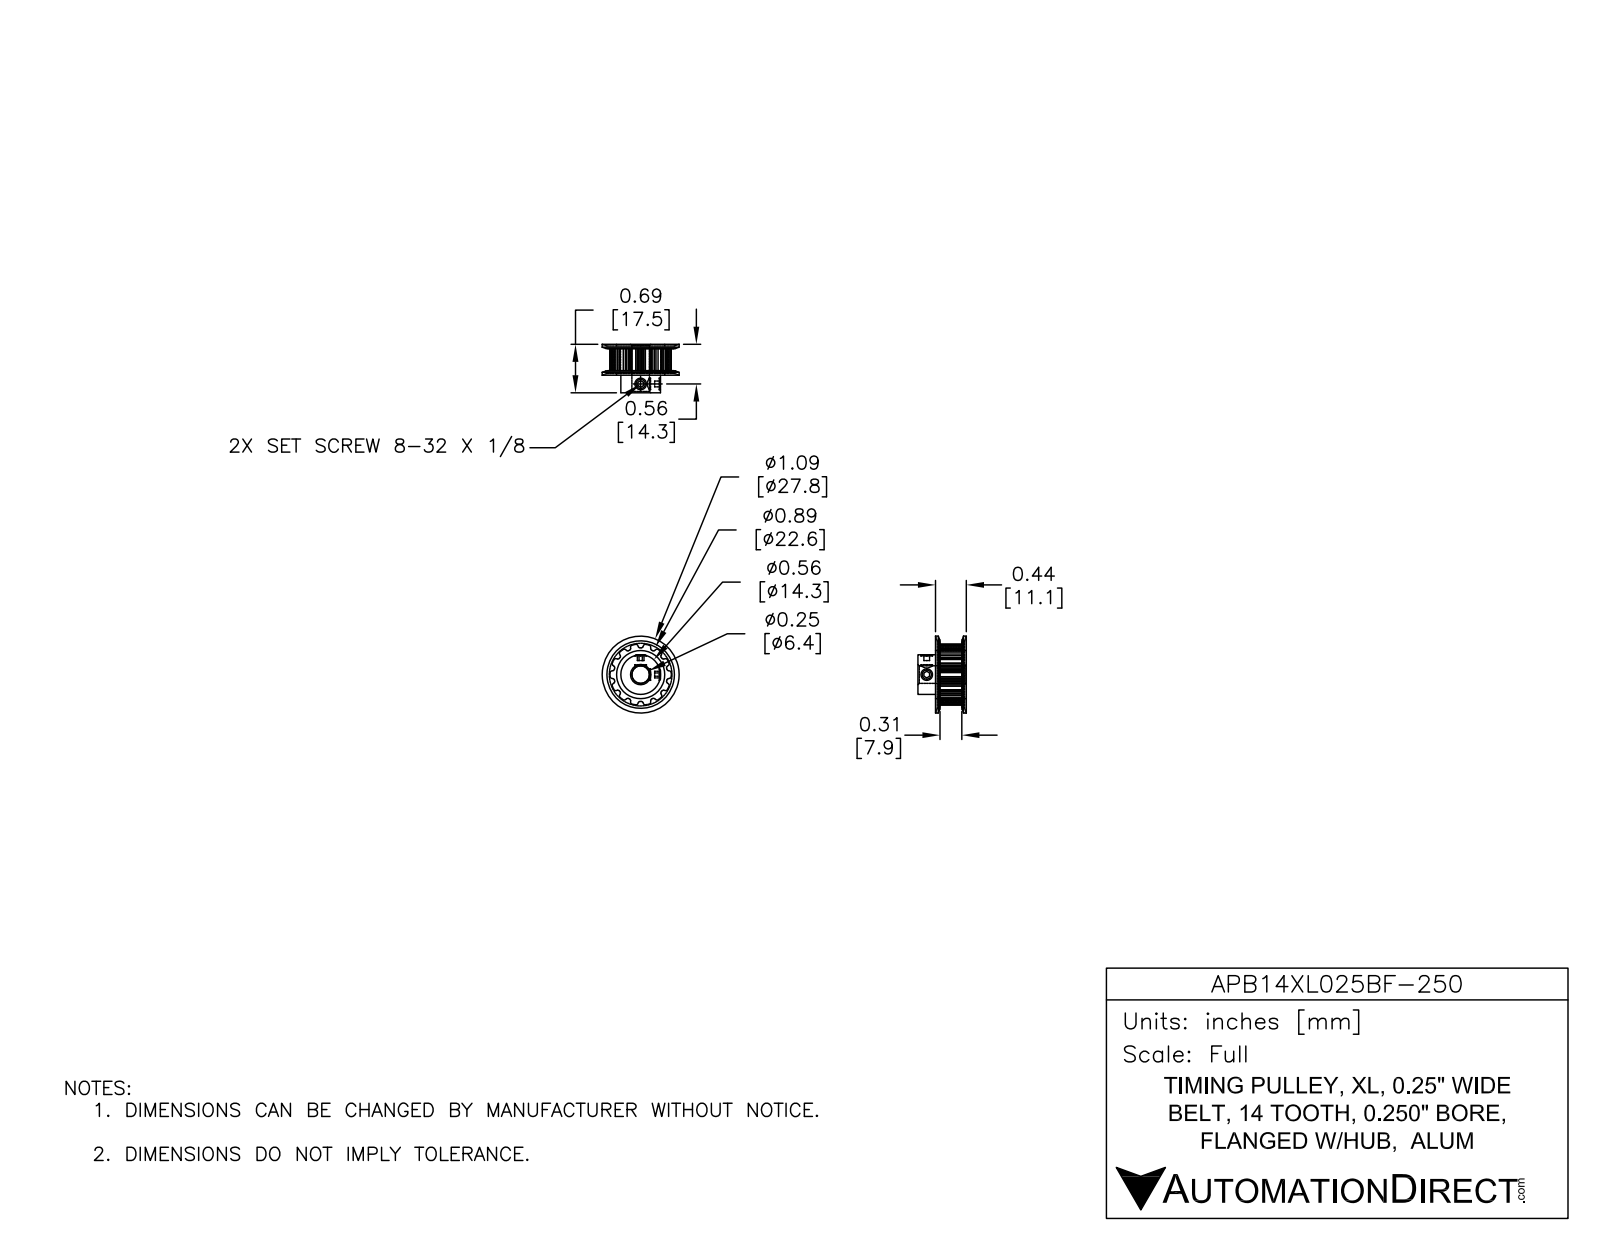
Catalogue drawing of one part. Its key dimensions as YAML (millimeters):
part_name: "APB14XL025BF-250"
step_written_by: "SolidWorks 2014 (AUTOMOTIVE_DESIGN)"
units: millimeters
bodies: {solids: 1, faces: 161, planar: 48, cylindrical: 91, other: 22}
overall_size: [27.8, 27.8, 17.5]
volume: 3720
surface_area: 3088
round_holes:
  - {diameter: 2.2, count: 2}
  - {diameter: 6.4, count: 1}
round_bosses_or_shafts:
  - {diameter: 9.5, count: 1}
partial_cylinders:
  - {radius: 0.4, count: 56}
  - {radius: 9.7, count: 1}
face_to_face_distances: [9.5, 0.8, 8.7, 22.1, 7, 7.9, 0.8, 1.7, 9.5, 10.3]
